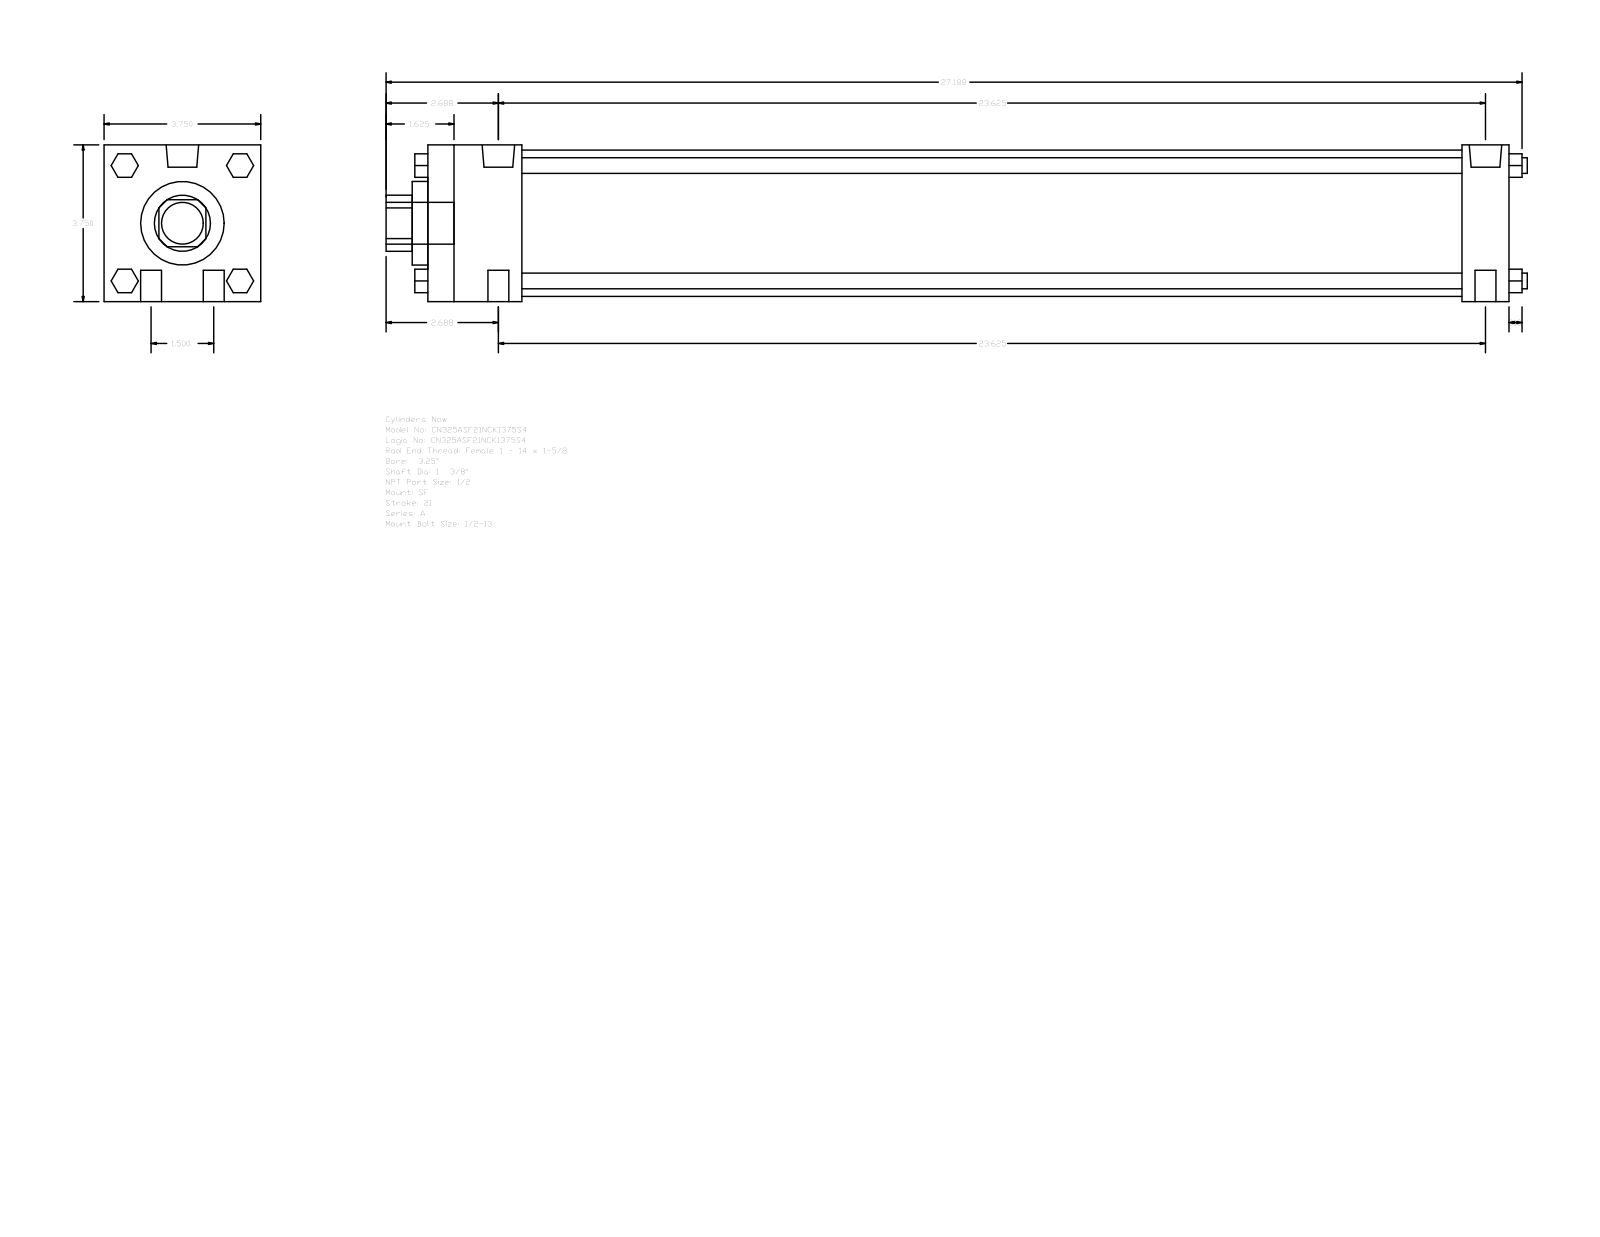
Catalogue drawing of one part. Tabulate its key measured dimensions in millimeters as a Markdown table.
| quantity | value |
| --- | --- |
| part name | A_SF__0325_1.375 |
| STEP written by | GSSL Pune (CONFIG_CONTROL_DESIGN) |
| units | millimeters |
| bodies | 0 solids, 124 faces (94 planar, 30 cylindrical, 0 other) |
| overall size | 693.74 × 95.25 × 95.25 |
| round holes (diameter × count) | 34.92 × 1, 50.8 × 1, 88.9 × 1 |
| round bosses / shafts (diameter × count) | 12.7 × 4, 9.53 × 4, 19.77 × 2, 8.73 × 2, 25.4 × 1 |
| partial cylindrical surfaces (radius × count) | 17.06 × 1 |
| main face-to-face distances | 95.24, 657.22, 28.57, 628.65, 57.15, 571.5, 600.07, 9.52, 66.67, 638.17 |
